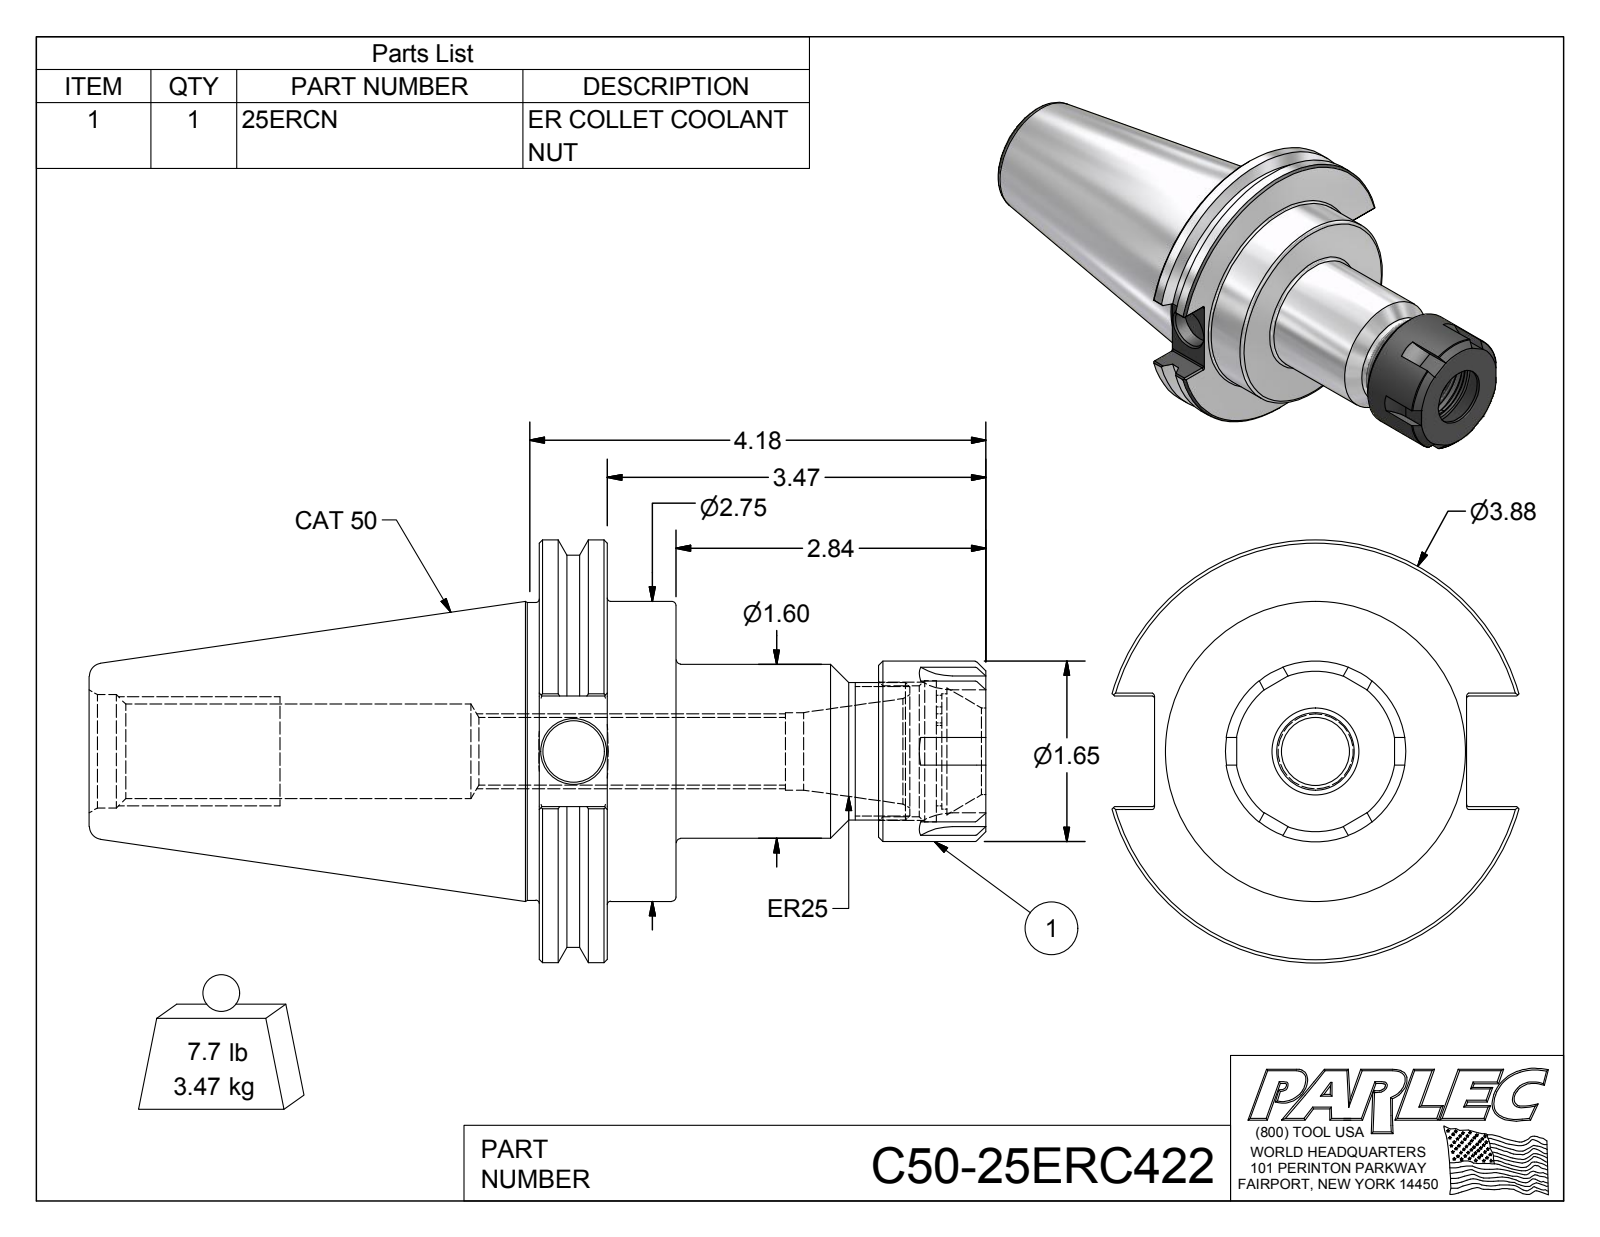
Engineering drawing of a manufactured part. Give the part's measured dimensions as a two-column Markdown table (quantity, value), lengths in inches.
| quantity | value |
| --- | --- |
| part name | C50-25ERC422; C50-25ER4-1; 25ERCN |
| STEP written by | Autodesk Inventor 2012 (AUTOMOTIVE_DESIGN) |
| units | inches |
| bodies | 2 solids, 137 faces (57 planar, 40 cylindrical, 40 other) |
| overall size | 8.22 × 3.875 × 3.729 |
| volume | 27.27 in³ |
| surface area | 99.85 in² |
| round holes (diameter × count) | 0.315 × 1, 0.399 × 1, 0.62 × 1, 0.71 × 1, 0.794 × 1, 0.865 × 1, 1.038 × 1, 1.057 × 1, 1.201 × 1, 1.294 × 1 |
| round bosses / shafts (diameter × count) | 3.875 × 1, 3.594 × 1, 2.75 × 1, 2.73 × 1, 1.654 × 1, 1.595 × 1, 1.26 × 1 |
| partial cylindrical surfaces (radius × count) | 0.02 × 8, 0.5 × 6, 0.472 × 1, 0.515 × 1 |
| main face-to-face distances | 0.625, 1.255, 0.63, 4.095, 3.47, 2.84, 3.111, 2.486, 1.856, 0.984 |
